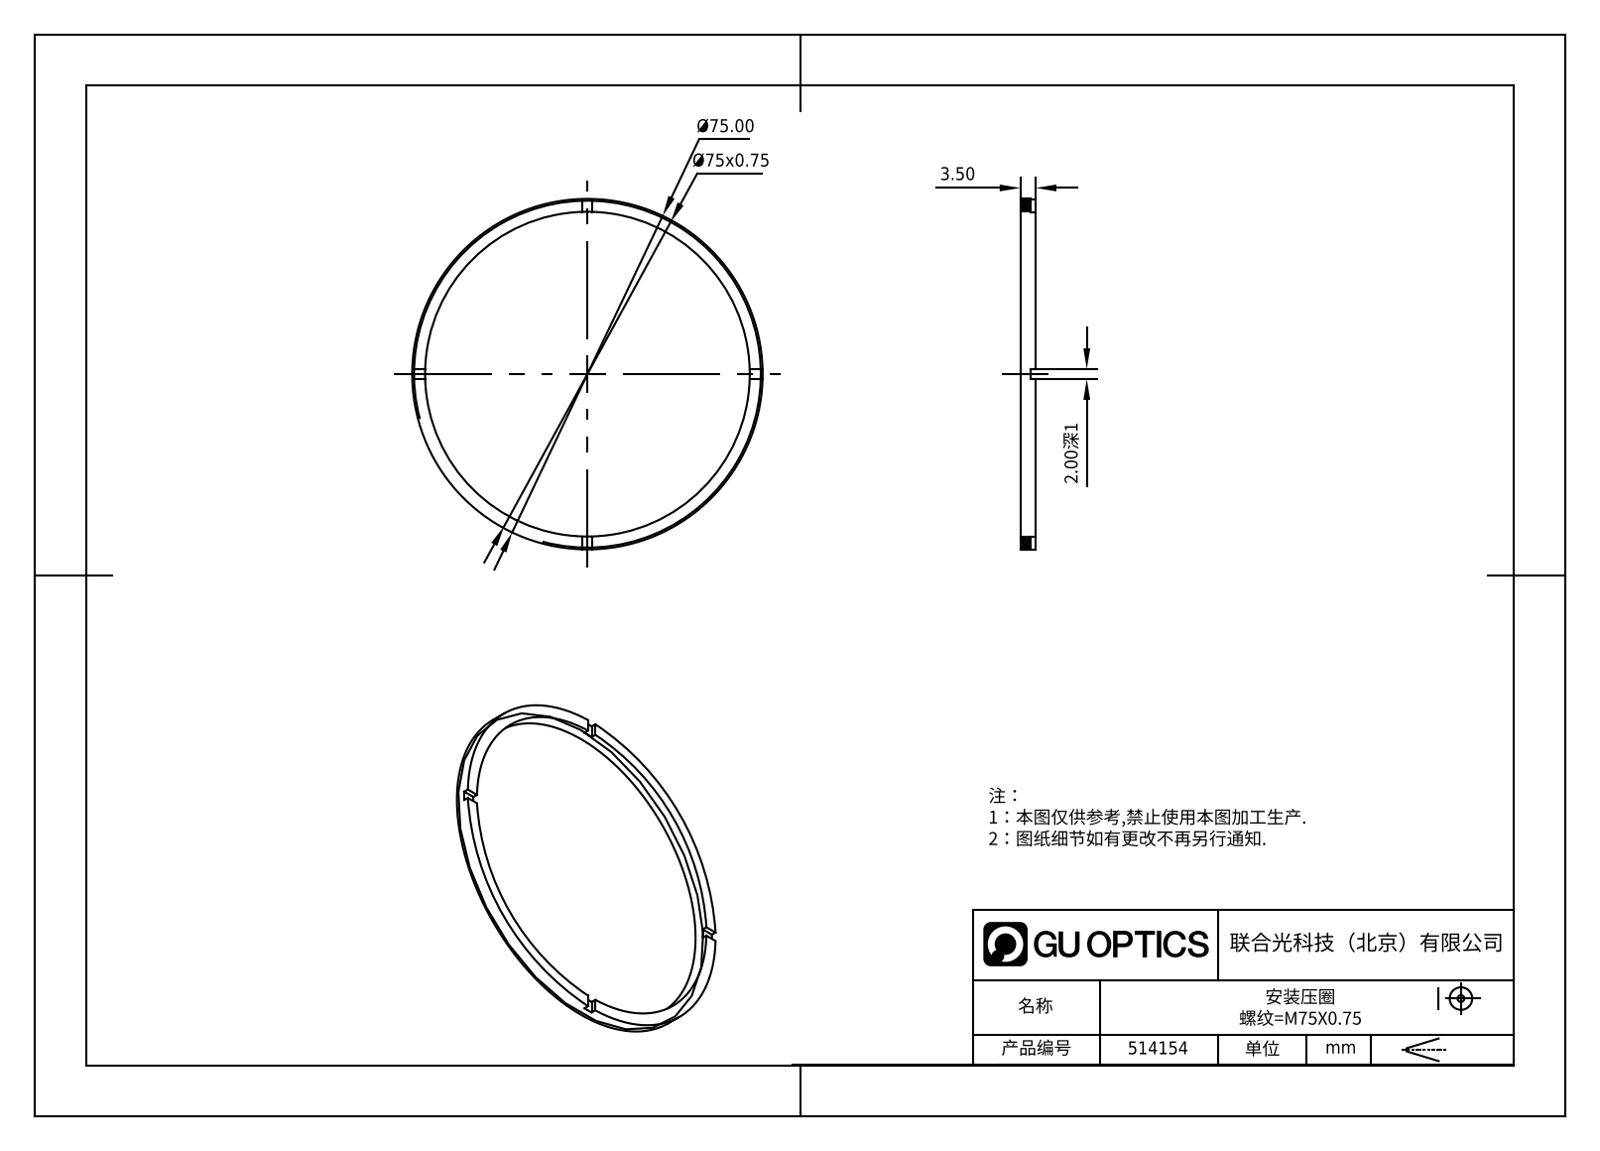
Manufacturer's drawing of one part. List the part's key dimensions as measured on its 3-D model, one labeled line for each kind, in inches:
Part name (STEP PRODUCT): 514154
STEP written by: SolidWorks 2020 (CONFIG_CONTROL_DESIGN)
Units: inches
Bodies: 1 solid, 21 faces (17 planar, 4 cylindrical, 0 other)
Overall size (bounding box): 2.953 × 2.953 × 0.138
Volume: 0.143 in³ · Surface area: 4.571 in²
Round holes (diameter × count): ⌀2.717 ×1
Round bosses / shafts (diameter × count): ⌀2.953 ×1
Main face-to-face distances: 0.138, 0.098, 0.039, 0.079
